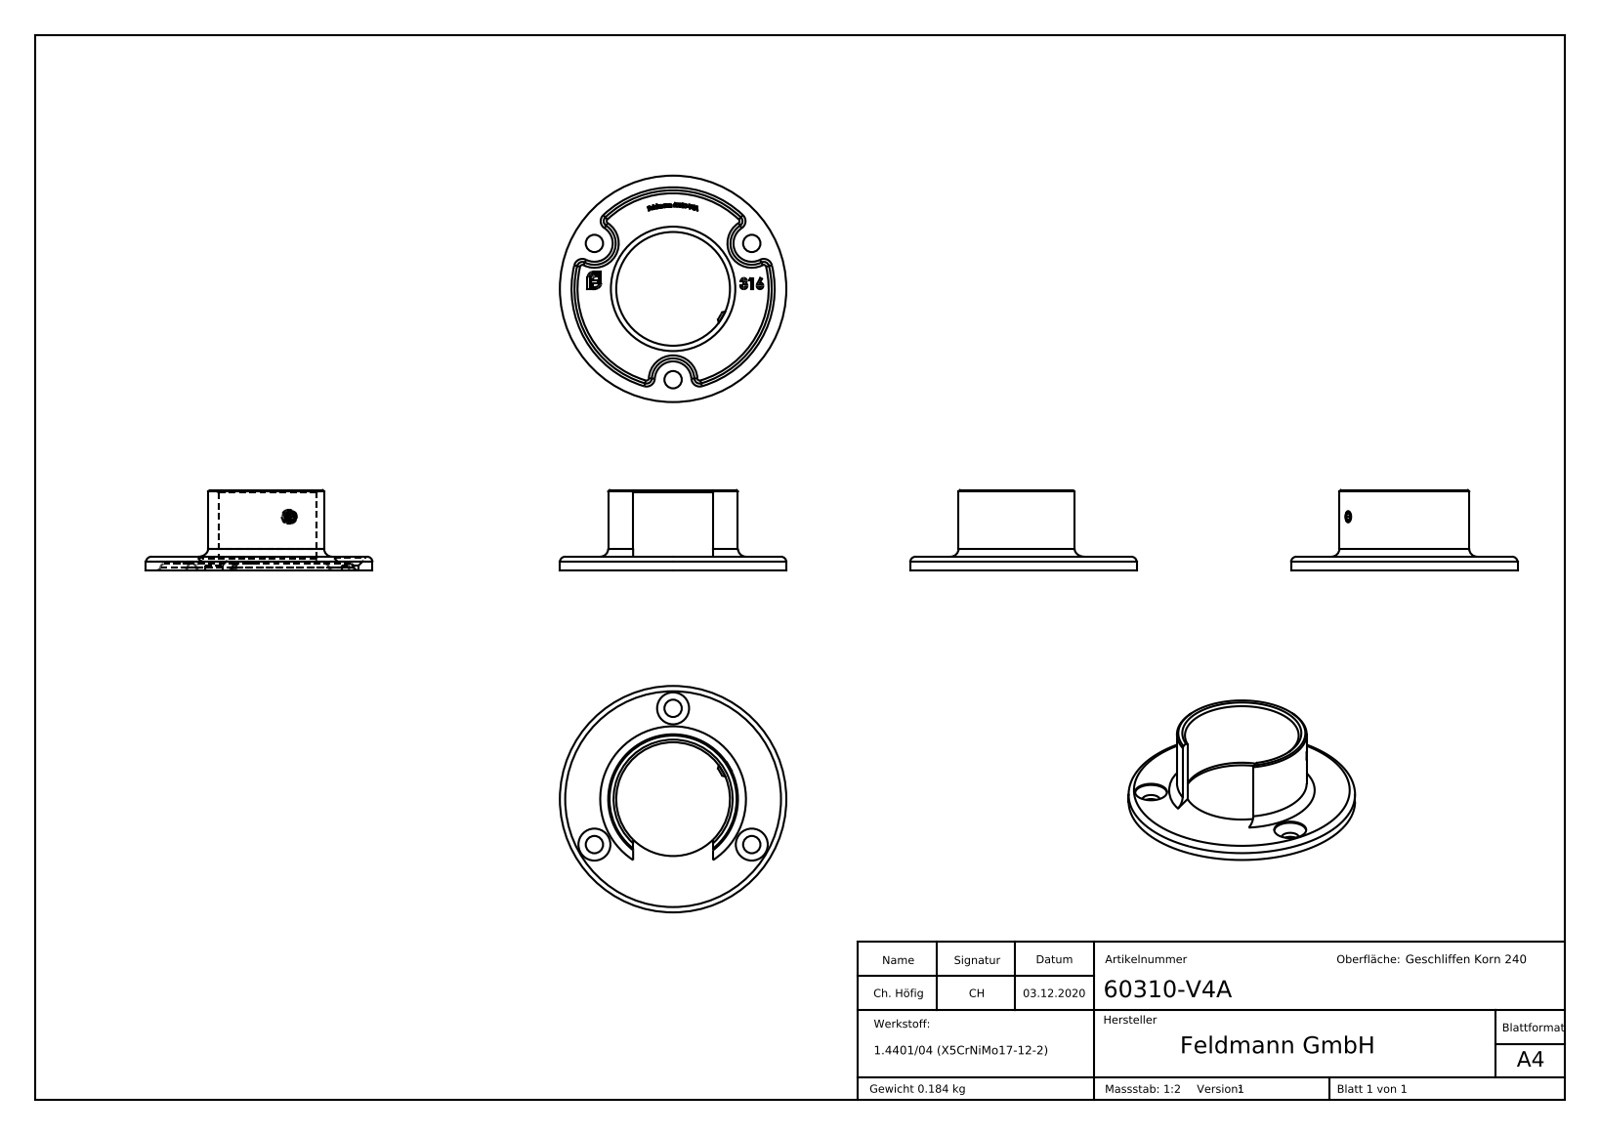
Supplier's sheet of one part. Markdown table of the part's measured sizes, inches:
| quantity | value |
| --- | --- |
| part name | DIN913; DIN913_DIN 913 M5x4; 60310-V4A; 60310-XXX Teil1 (+1 more) |
| STEP written by | SolidWorks 2018 (CONFIG_CONTROL_DESIGN) |
| units | inches |
| bodies | 2 solids, 389 faces (183 planar, 22 cylindrical, 184 other) |
| overall size | 3.346 × 3.346 × 1.181 |
| volume | 1.402 in³ |
| surface area | 24.62 in² |
| round holes (diameter × count) | 0.256 × 3, 0.472 × 3, 0.165 × 1, 1.681 × 1 |
| round bosses / shafts (diameter × count) | 3.346 × 1, 0.197 × 1 |
| partial cylindrical surfaces (radius × count) | 0.959 × 1 |
| main face-to-face distances | 0.108, 0.089, 0.197, 1.181, 1.093, 0.984, 0.104, 0.093, 1.089, 0.098 |
| hole center spacings | 1.343, 2.325 |
